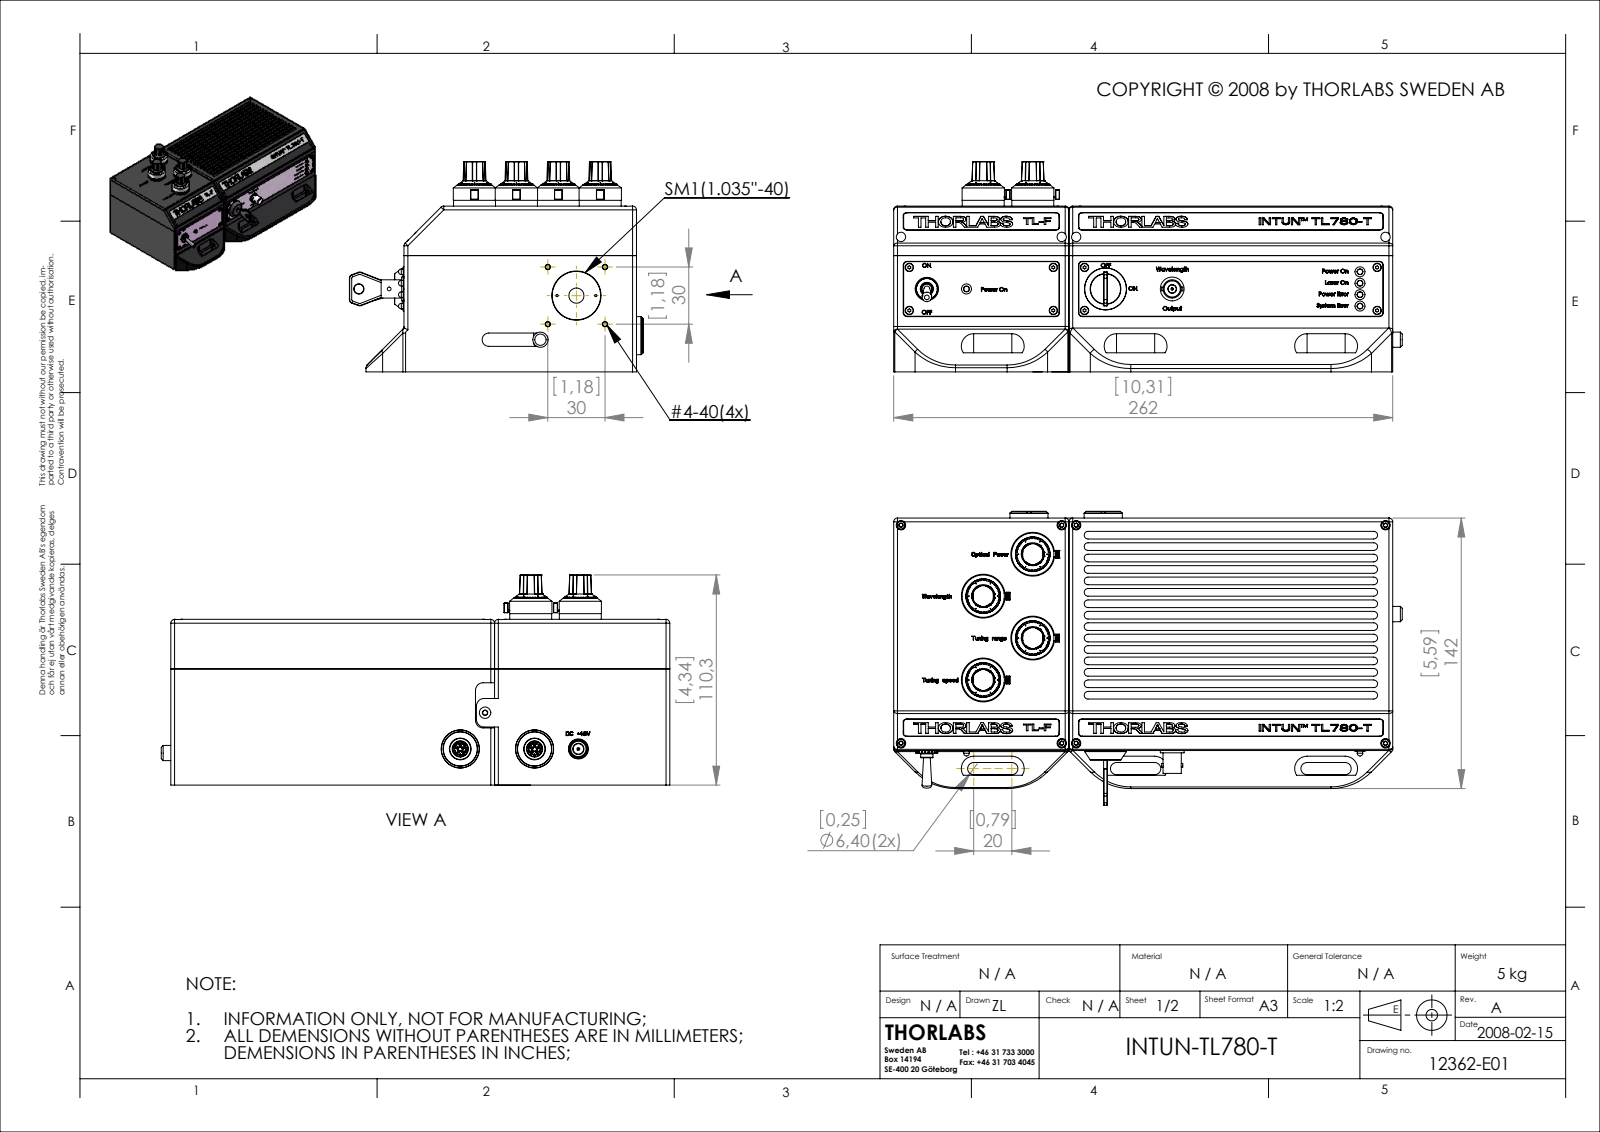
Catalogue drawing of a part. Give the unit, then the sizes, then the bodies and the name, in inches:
Units: inches
Overall size (bounding box): 10.512 × 6.071 × 4.343
Round holes (diameter × count): ⌀0.039 ×33, ⌀0.106 ×17, ⌀0.081 ×13, ⌀0.094 ×12, ⌀0.063 ×8, ⌀0.114 ×8, ⌀0.193 ×8, ⌀0.087 ×6, ⌀0.433 ×6, ⌀0.118 ×5, ⌀0.169 ×5, ⌀0.177 ×5
Round bosses / shafts (diameter × count): ⌀0.079 ×11, ⌀0.157 ×8, ⌀0.224 ×6, ⌀0.209 ×6, ⌀0.118 ×6, ⌀0.098 ×6, ⌀0.866 ×5, ⌀0.244 ×5
Partial cylindrical surfaces — rounded edges, fillets, slot ends (radius × count): R0.079 ×89, R0.197 ×37, R0.006 ×20, R0.039 ×20, R0.071 ×16, R0.008 ×14, R0.039 ×12, R0.236 ×12
Main face-to-face distances: 0.197, 0.039, 0.118, 0.236, 0.079, 0.246, 3.425, 3.386, 0.22, 3.307
Hole centre spacings: 0.126, 0.136, 0.191, 0.25, 0.071, 0.229, 1.341, 1.732
Bodies: 0 solids, 7368 faces (5097 planar, 1137 cylindrical, 1134 other)
Part name (STEP PRODUCT): INTUN-TL780-T
STEP written by: SolidWorks 2007 (CONFIG_CONTROL_DESIGN)
